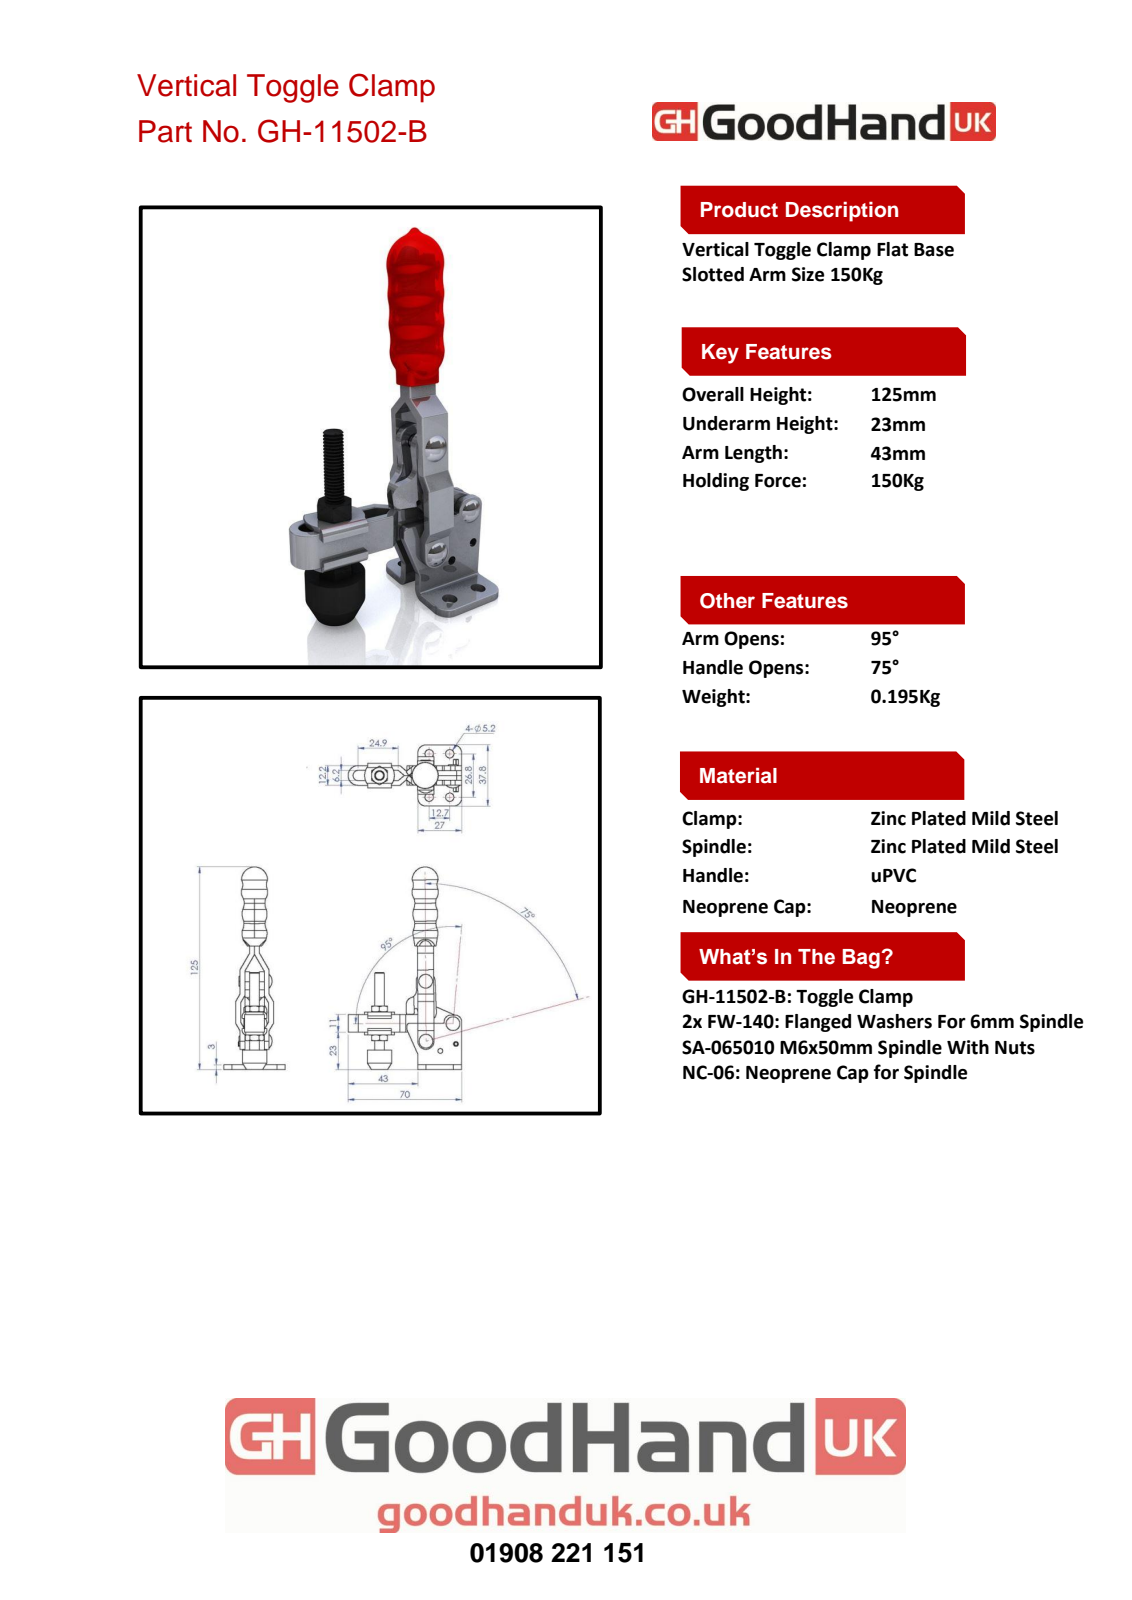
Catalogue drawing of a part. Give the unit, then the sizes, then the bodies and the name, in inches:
Units: inches
Overall size (bounding box): 4.922 × 2.756 × 1.488
Round holes (diameter × count): ⌀0.118 ×4, ⌀0.205 ×4
Round bosses / shafts (diameter × count): ⌀0.191 ×2, ⌀0.591 ×1, ⌀0.236 ×1
Partial cylindrical surfaces — rounded edges, fillets, slot ends (radius × count): R0.039 ×9, R0.197 ×6, R0.102 ×4, R0.079 ×2, R0.209 ×2, R0.228 ×2, R0.059 ×1, R0.122 ×1
Main face-to-face distances: 0.118, 0.236, 0.354, 0.472, 0.122, 0.24, 0.358, 0.476, 0.114, 0.217
Hole centre spacings: 0.5, 1.055, 1.168, 0.689, 0.705, 0.753, 0.783, 1.227
Volume: 1.913 in³ · Surface area: 34 in²
Bodies: 8 solids, 305 faces (145 planar, 92 cylindrical, 68 other)
Part name (STEP PRODUCT): 111502B08-1^493780(GH-11502-B); Group5^493780(GH-11502-B); Group4^493780(GH-11502-B); Group2^493780(GH-11502-B) (+2 more)
STEP written by: SolidWorks 2016 (AUTOMOTIVE_DESIGN)
